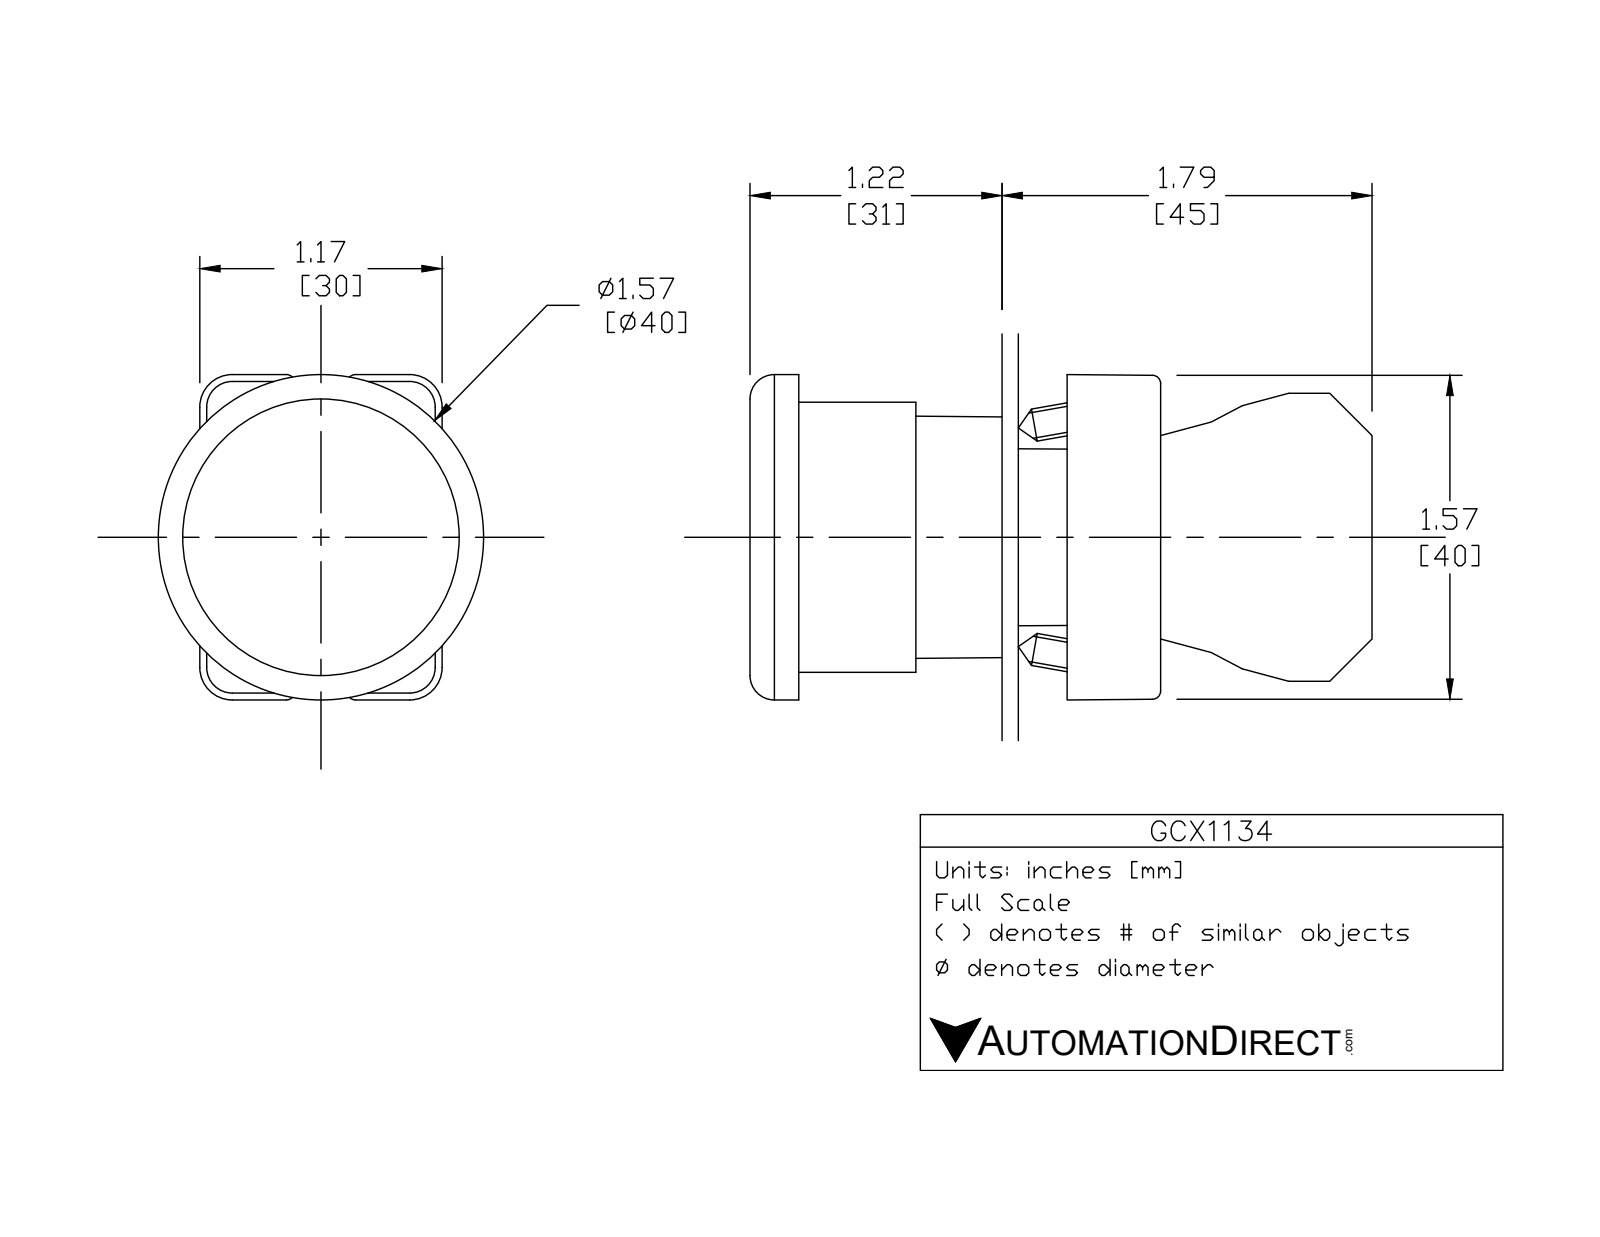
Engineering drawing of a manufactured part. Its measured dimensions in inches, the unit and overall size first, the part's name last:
Units: inches
Overall size (bounding box): 2.944 × 1.581 × 1.575
Round holes (diameter × count): ⌀0.079 ×2, ⌀0.124 ×2, ⌀0.13 ×2, ⌀0.087 ×1, ⌀0.197 ×1, ⌀0.878 ×1, ⌀0.888 ×1, ⌀1.024 ×1, ⌀1.181 ×1
Round bosses / shafts (diameter × count): ⌀0.157 ×2, ⌀1.575 ×1, ⌀1.299 ×1, ⌀1.175 ×1, ⌀0.945 ×1, ⌀0.856 ×1, ⌀0.78 ×1
Partial cylindrical surfaces — rounded edges, fillets, slot ends (radius × count): R0.059 ×24, R0.041 ×12, R0.124 ×12, R0.157 ×12, R0.039 ×4, R0.128 ×2, R0.02 ×1, R0.063 ×1
Main face-to-face distances: 1.921, 0.579, 0.033, 1.763, 0.157, 1.724, 0.031, 1.024, 0.76, 1.004
Hole centre spacings: 0.236, 0.544, 0.472, 0.49
Volume: 1.871 in³ · Surface area: 33.58 in²
Bodies: 6 solids, 389 faces (224 planar, 136 cylindrical, 29 other)
Part name (STEP PRODUCT): GCX1134 OPERATOR; ECX1029-2; ecx1040; GCX1134
STEP written by: SolidWorks 2016 (AUTOMOTIVE_DESIGN)
